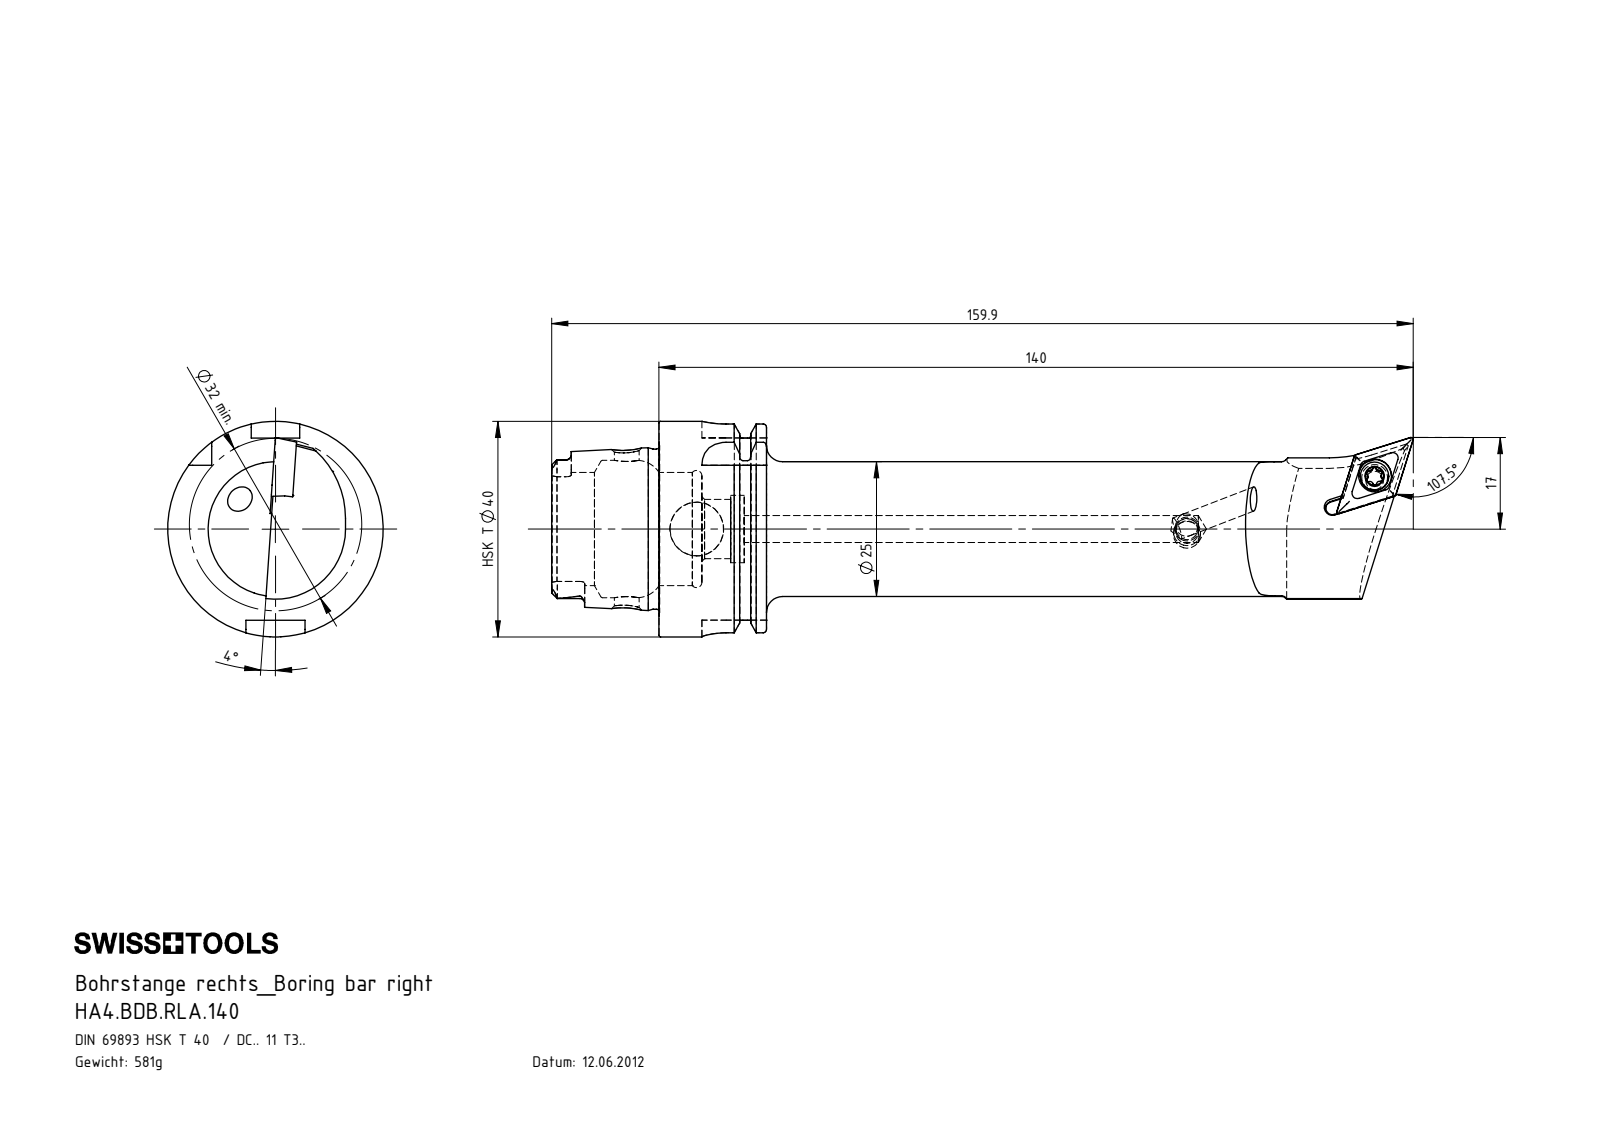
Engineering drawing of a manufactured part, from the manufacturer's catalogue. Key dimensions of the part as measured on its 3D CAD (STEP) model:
Part name (STEP PRODUCT): DCMT11T304; WCB-ER2.001.009_A; HA4.BDB.RLA.140; HA4-BDB.RLA.140_A (+1 more)
STEP written by: SolidWorks 2017 (AUTOMOTIVE_DESIGN)
Units: millimetres
Bodies: 5 solids, 310 faces (77 planar, 90 cylindrical, 143 other)
Overall size (bounding box): 159.9 × 40 × 40
Volume: 73 786 mm³ · Surface area: 20 802 mm²
Round holes (diameter × count): ⌀4.2 ×2, ⌀5 ×2, ⌀3.3 ×1, ⌀4 ×1, ⌀4.4 ×1, ⌀4.6 ×1, ⌀6.1 ×1, ⌀10 ×1, ⌀11 ×1, ⌀12.5 ×1, ⌀21 ×1, ⌀25.5 ×1
Round bosses / shafts (diameter × count): ⌀40 ×1, ⌀34.75 ×1, ⌀29.71 ×1, ⌀25 ×1, ⌀5.25 ×1, ⌀5 ×1, ⌀4 ×1
Partial cylindrical surfaces — rounded edges, fillets, slot ends (radius × count): R0.34 ×6, R0.59 ×6, R0.9 ×6, R1.88 ×4, R4.5 ×4, R1.25 ×1, R3 ×1, R13 ×1
Main face-to-face distances: 19.95, 7.95, 12, 3.66, 19.9, 27.85, 39.85, 35.7, 15.8, 7.85
